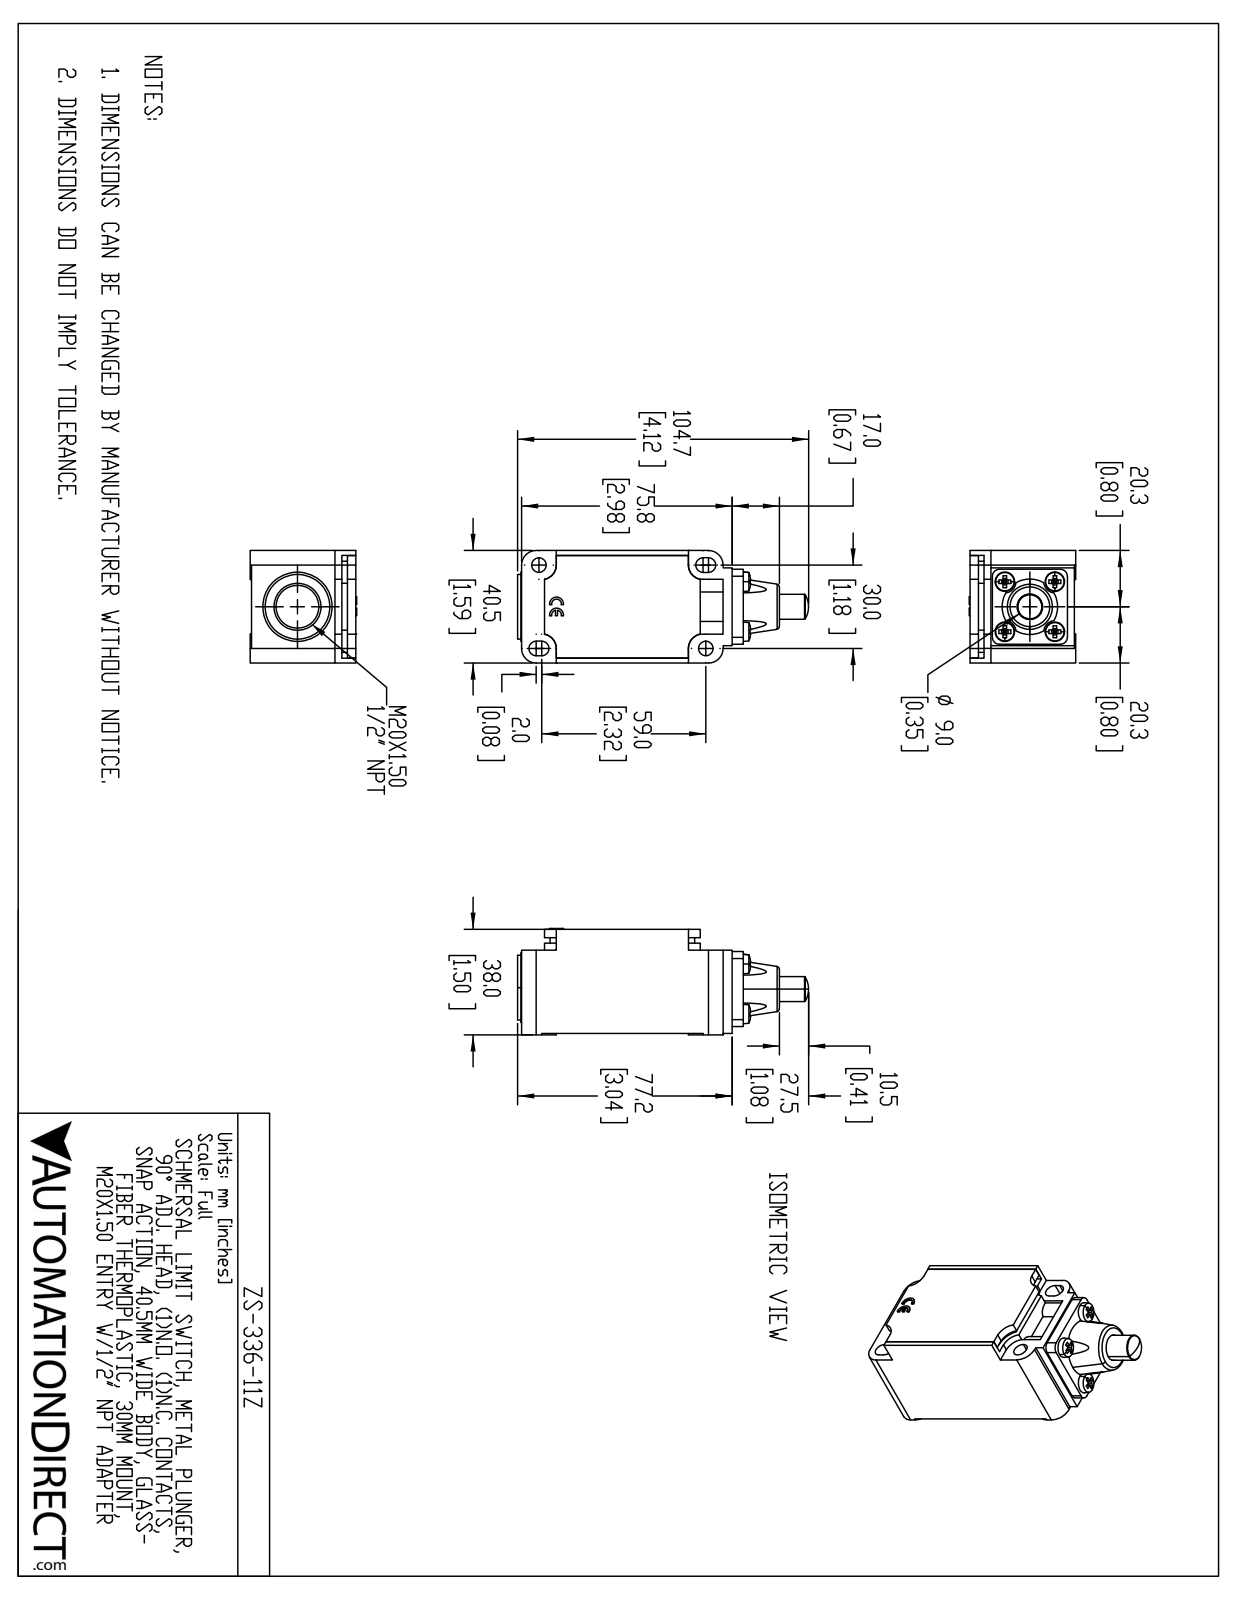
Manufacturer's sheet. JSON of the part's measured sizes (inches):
{"part_name": "ZS-336-11Z-M20", "step_written_by": "SolidWorks 2019 (AUTOMOTIVE_DESIGN)", "units": "inches", "bodies": {"solids": 1, "faces": 255, "planar": 171, "cylindrical": 58, "other": 26}, "overall_size": [4.122, 1.594, 1.508], "volume_in3": 6.556, "surface_area_in2": 31.56, "round_holes": [[0.209, 2], [0.362, 1], [0.669, 1]], "round_bosses_or_shafts": [[0.984, 1], [0.917, 1], [0.354, 1]], "partial_cylinders_radius": [[0.205, 8], [0.207, 8], [0.098, 6], [0.104, 4], [0.157, 4], [0.283, 4], [0.069, 2]], "face_to_face_distances": [1.594, 1.476, 1.181, 0.295, 0.118, 0.197, 0.079, 0.02, 1.28, 0.177], "hole_center_spacings": [0.02, 2.641]}
